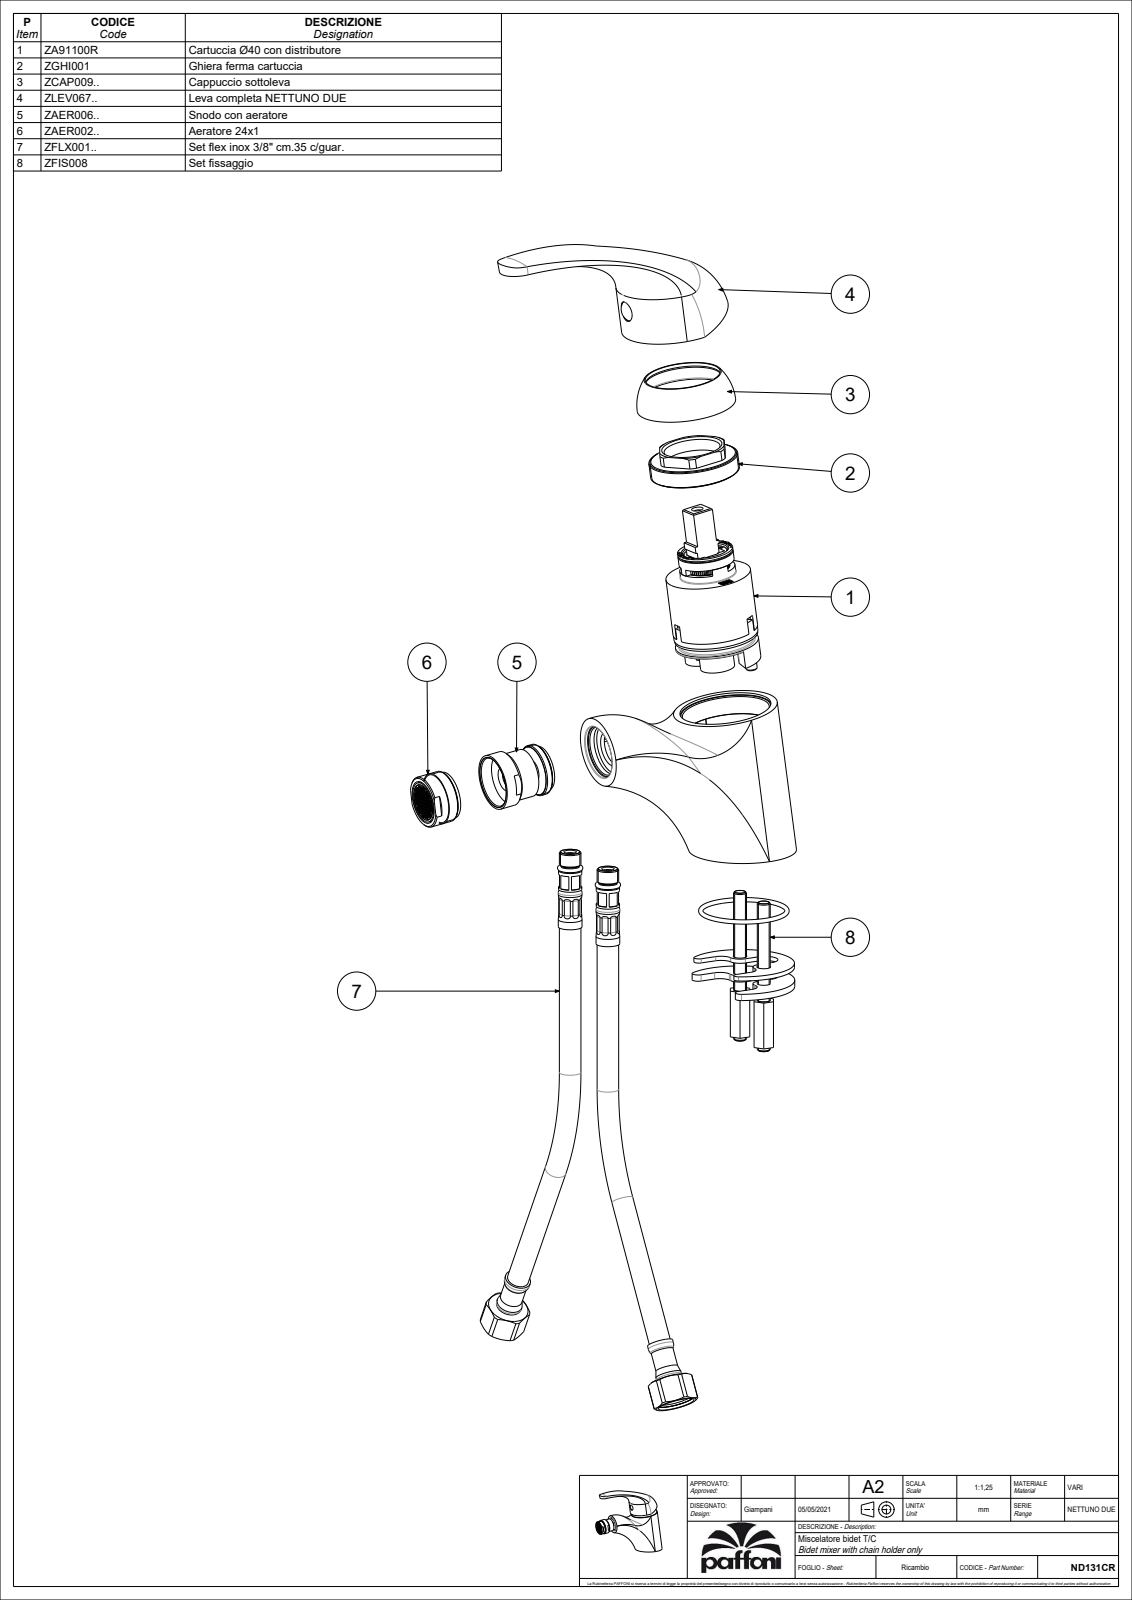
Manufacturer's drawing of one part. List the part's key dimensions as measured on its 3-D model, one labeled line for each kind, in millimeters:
Part name (STEP PRODUCT): ND131CR
STEP written by: CREO PARAMETRIC BY PTC INC, 2020044 (CONFIG_CONTROL_DESIGN)
Units: millimetres
Bodies: 1 solid, 305 faces (107 planar, 88 cylindrical, 110 other)
Overall size (bounding box): 132.93 × 117.65 × 51
Volume: 133 672 mm³ · Surface area: 65 420 mm²
Round holes (diameter × count): ⌀5 ×2, ⌀5.5 ×2, ⌀7 ×2, ⌀9 ×2, ⌀11 ×2, ⌀6 ×1, ⌀8 ×1, ⌀15.5 ×1, ⌀16 ×1, ⌀23 ×1, ⌀35 ×1, ⌀39.1 ×1
Round bosses / shafts (diameter × count): ⌀8 ×2, ⌀25.8 ×1, ⌀24 ×1, ⌀22.5 ×1, ⌀21 ×1, ⌀10 ×1, ⌀5 ×1
Partial cylindrical surfaces — rounded edges, fillets, slot ends (radius × count): R2 ×10, R1 ×2, R6 ×2, R7.5 ×2, R3.9 ×1, R4 ×1, R19 ×1
Main face-to-face distances: 4.5, 3.51, 60.94, 60.98, 6, 2, 3.5, 65.44, 65.48, 10.99
Hole centre spacings: 8.59, 8.6, 11.49, 11.81, 13.46, 15.62, 15.63, 15.81
